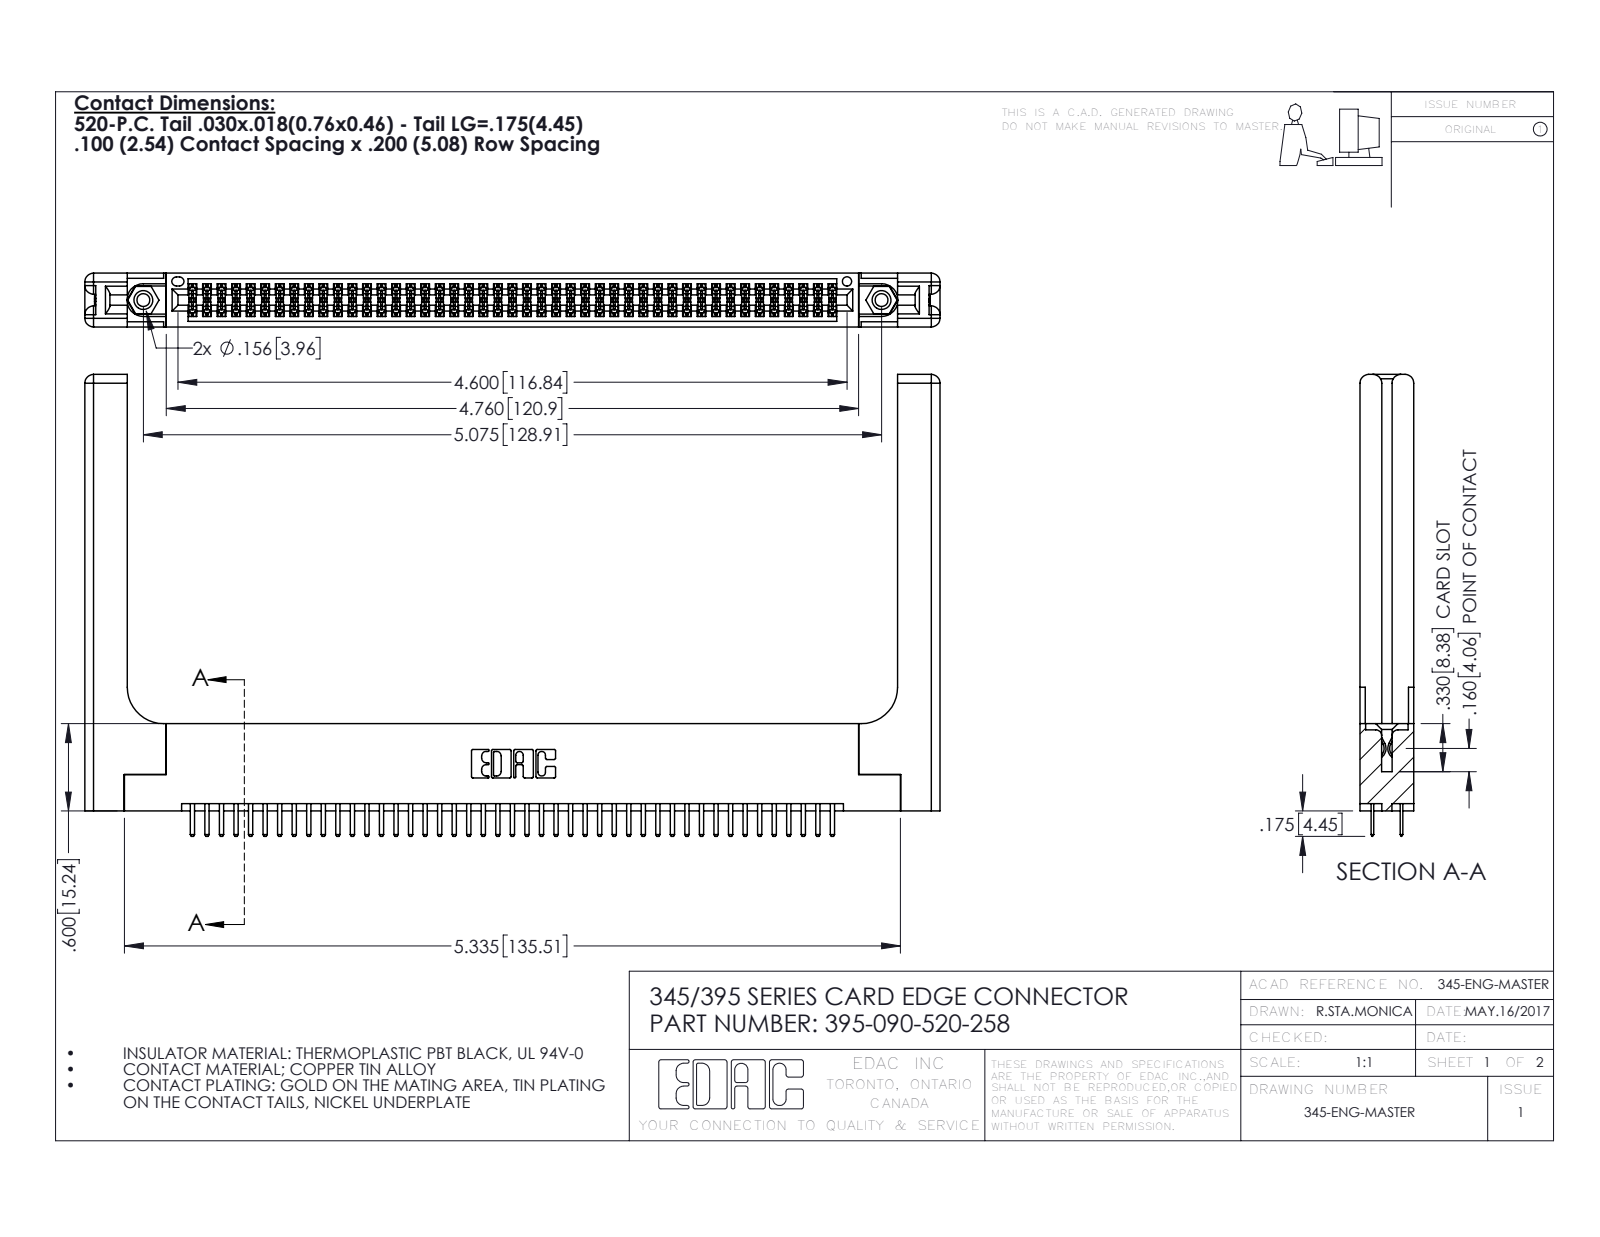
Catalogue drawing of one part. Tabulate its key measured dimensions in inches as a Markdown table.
| quantity | value |
| --- | --- |
| part name | 345-250-001_345-250-001-102; 345-292-001_345-293-120; 395-090-520-258; 345 Part_Flush Mounting Lugs - 0.156 Dia-TH (+1 more) |
| STEP written by | SolidWorks 2016 (CONFIG_CONTROL_DESIGN) |
| units | inches |
| bodies | 95 solids, 5242 faces (3378 planar, 1804 cylindrical, 60 other) |
| overall size | 5.879 × 3.175 × 0.37 |
| volume | 1.402 in³ |
| surface area | 41.01 in² |
| round holes (diameter × count) | 0.089 × 2, 0.125 × 2, 0.156 × 2, 0.064 × 1 |
| round bosses / shafts (diameter × count) | 0.155 × 2 |
| partial cylindrical surfaces (radius × count) | 0.006 × 135, 0.01 × 94, 0.01 × 22, 0.06 × 16, 0.007 × 6, 0.031 × 6, 0.026 × 3, 0.014 × 2 |
| main face-to-face distances | 0.072, 0.37, 0.298, 0.2, 0.098, 0.272, 0.025, 0.225, 0.148, 0.15 |
| hole center spacings | 0.27, 4.839, 5.075 |
